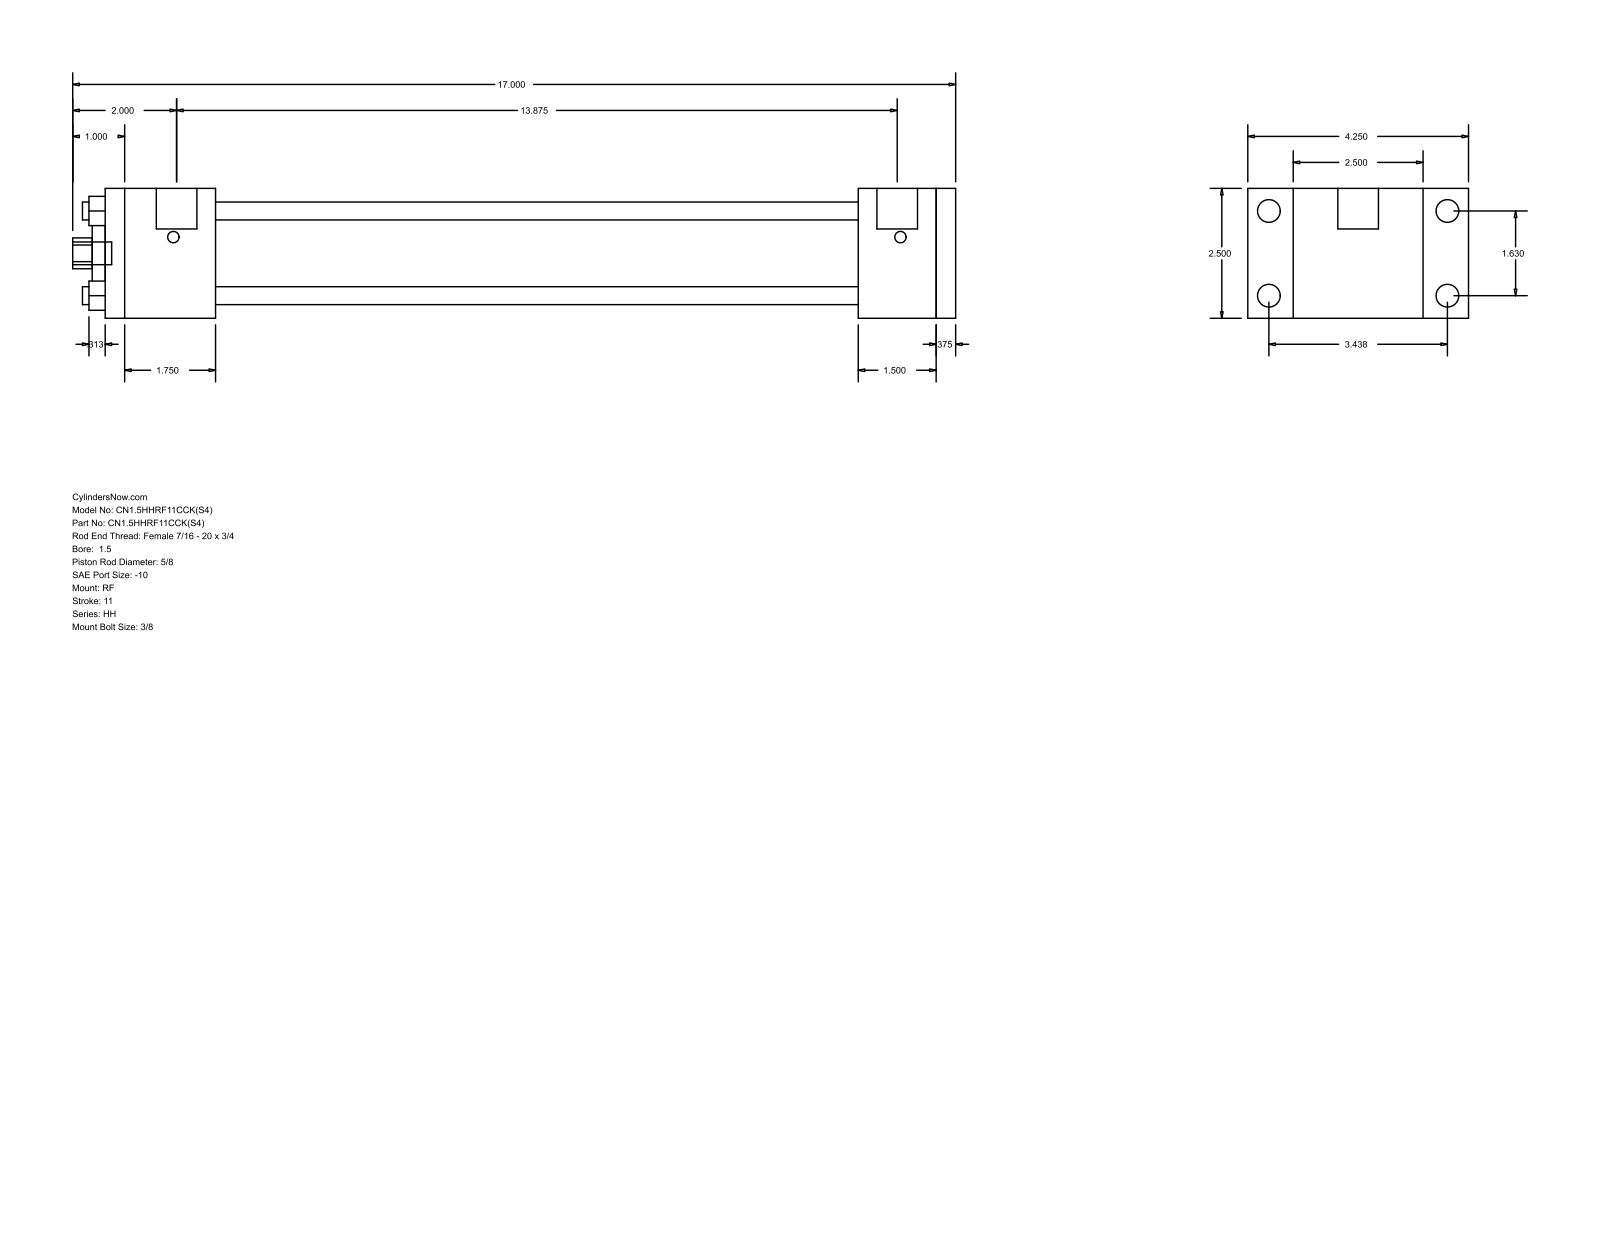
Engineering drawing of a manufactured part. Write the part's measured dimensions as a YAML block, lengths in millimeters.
part_name: "HH_RF__0150_0.625"
step_written_by: "GSSL Pune (CONFIG_CONTROL_DESIGN)"
units: millimeters
bodies: {solids: 0, faces: 92, planar: 64, cylindrical: 28, other: 0}
overall_size: [431.8, 107.95, 63.5]
round_holes:
  - {diameter: 8.76, count: 4}
  - {diameter: 15.88, count: 1}
  - {diameter: 28.57, count: 1}
  - {diameter: 44.45, count: 1}
round_bosses_or_shafts:
  - {diameter: 11.13, count: 4}
  - {diameter: 5.56, count: 4}
  - {diameter: 19.84, count: 2}
  - {diameter: 11.11, count: 1}
partial_cylinders:
  - {radius: 7.54, count: 1}
face_to_face_distances: [63.5, 415.92, 9.53, 406.39, 53.97, 368.3, 314.33, 352.42, 361.95, 38.09]
hole_center_spacings: [29.27, 41.4, 58.55]
